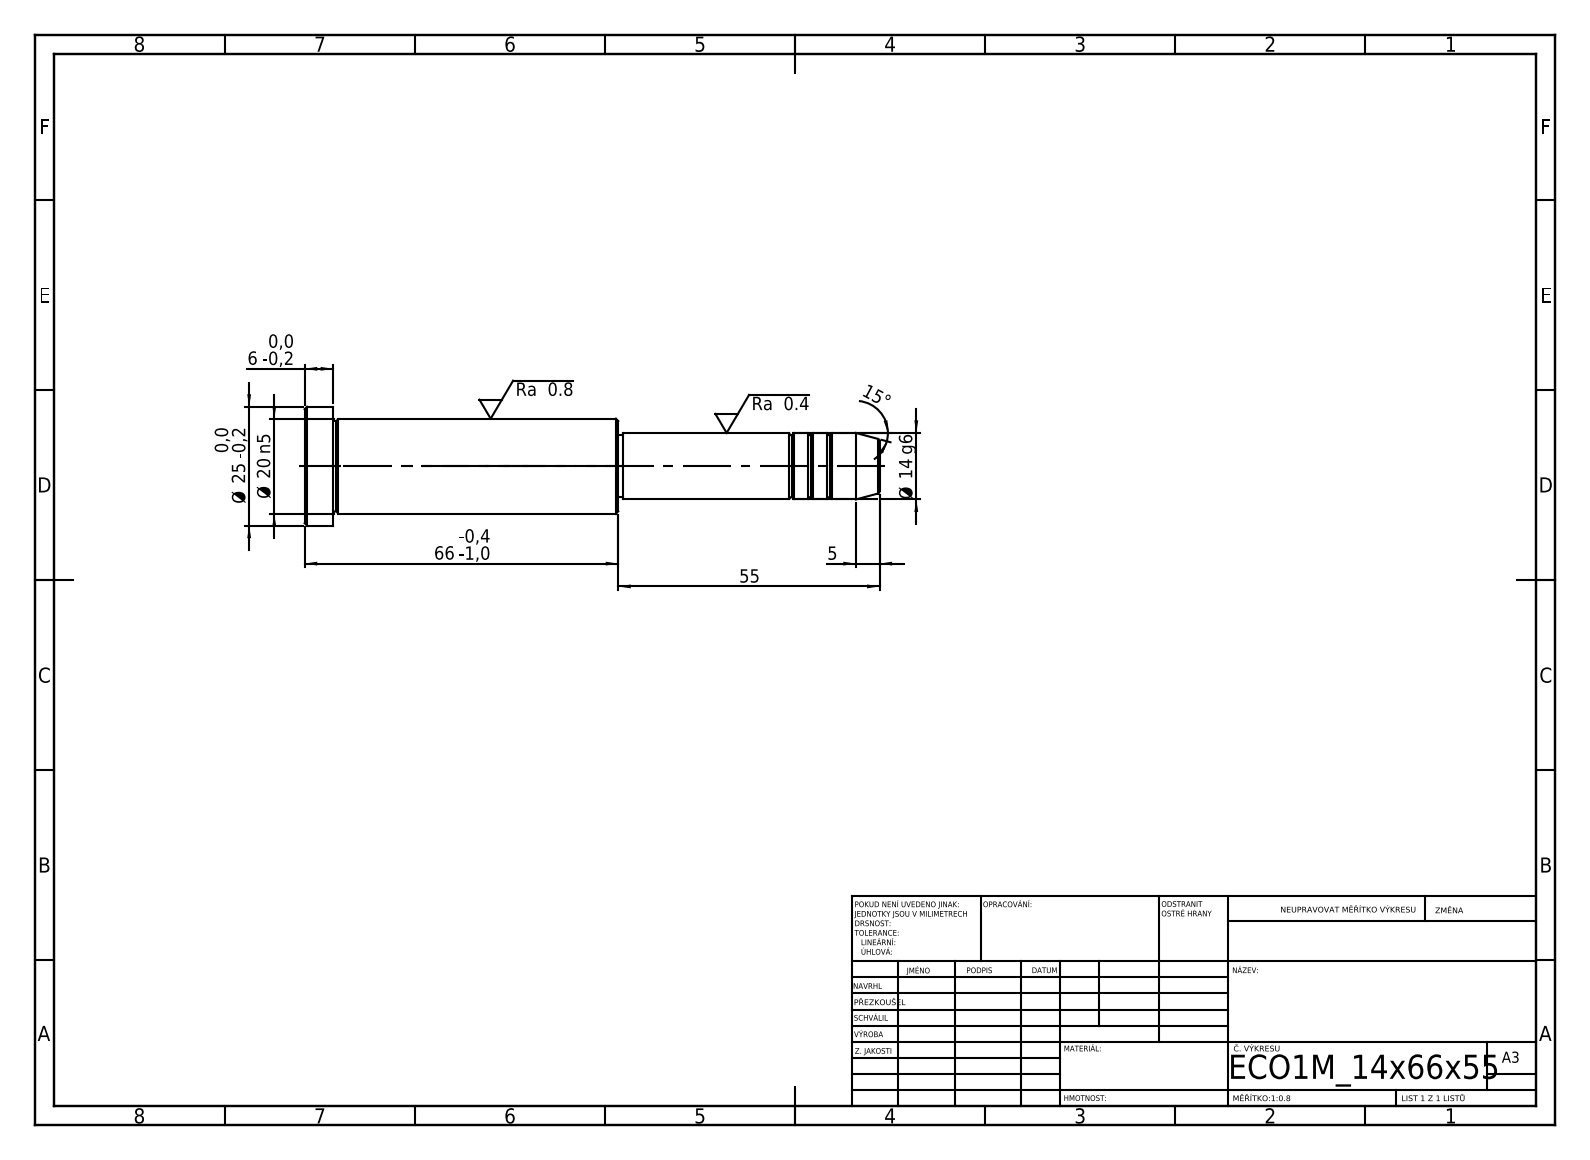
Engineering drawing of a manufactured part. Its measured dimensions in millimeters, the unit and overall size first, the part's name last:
Units: millimetres
Overall size (bounding box): 121 × 25 × 25
Round bosses / shafts (diameter × count): ⌀25 ×1, ⌀20 ×1, ⌀14 ×1, ⌀13 ×1
Main face-to-face distances: 6, 60, 66, 55, 115, 121, 54, 1, 61, 67
Volume: 30 009 mm³ · Surface area: 7 666 mm²
Bodies: 1 solid, 43 faces (5 planar, 14 cylindrical, 24 other)
STEP written by: SolidWorks 2019 (CONFIG_CONTROL_DESIGN)
